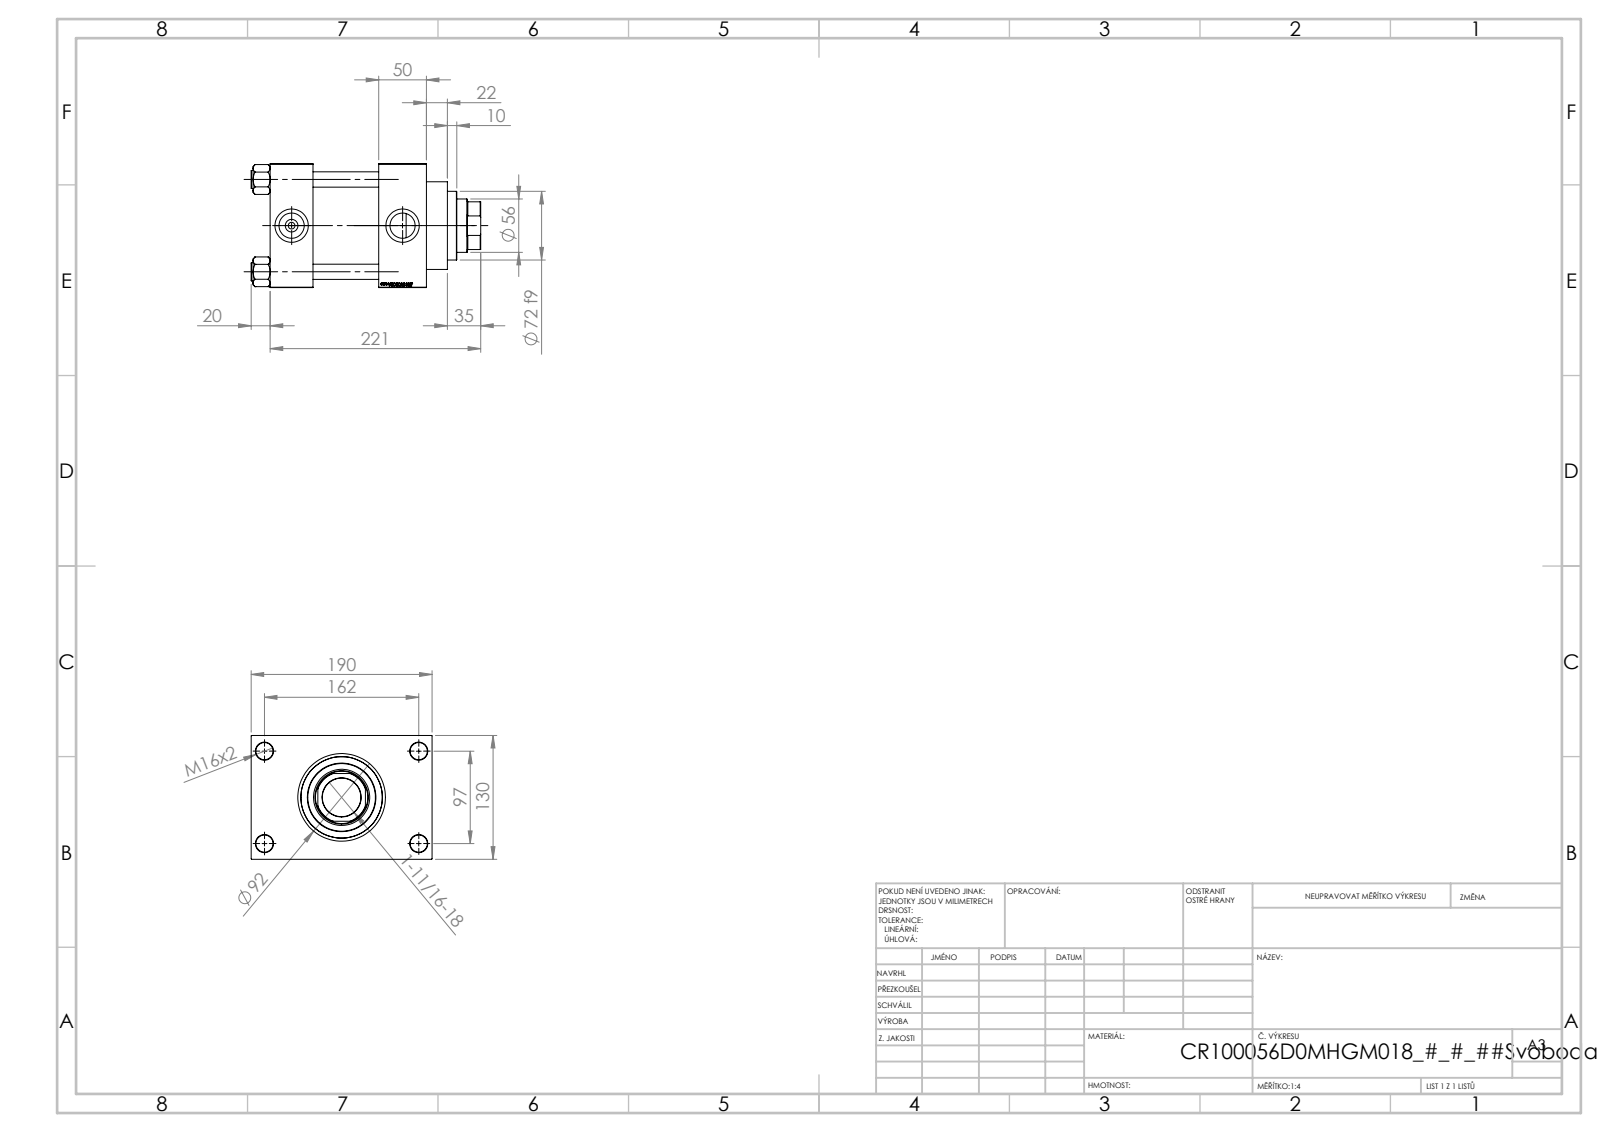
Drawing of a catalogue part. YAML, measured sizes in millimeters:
part_name: "V215CR_VCP_D; V215CR_D_TYCINKA; V215CR_D_Body; V215_VC_A (+1 more)"
step_written_by: "SolidWorks 2019 (CONFIG_CONTROL_DESIGN)"
units: millimeters
bodies: {solids: 11, faces: 1151, planar: 545, cylindrical: 88, other: 518}
overall_size: [241, 190, 130]
volume: 2620000
surface_area: 360315
round_holes:
  - {diameter: 16, count: 4}
  - {diameter: 18, count: 4}
  - {diameter: 7, count: 2}
  - {diameter: 26.44, count: 2}
  - {diameter: 35, count: 2}
  - {diameter: 40.5, count: 1}
  - {diameter: 56, count: 1}
  - {diameter: 59, count: 1}
  - {diameter: 76, count: 1}
  - {diameter: 85.5, count: 1}
  - {diameter: 100, count: 1}
round_bosses_or_shafts:
  - {diameter: 19, count: 4}
  - {diameter: 106, count: 1}
  - {diameter: 92, count: 1}
  - {diameter: 72, count: 1}
partial_cylinders:
  - {radius: 27, count: 1}
face_to_face_distances: [130, 69, 114, 50, 45, 164, 119, 30, 160, 18]
hole_center_spacings: [32.55, 68.52, 94.41, 96.9, 102.27, 129.45, 161.73, 97]
